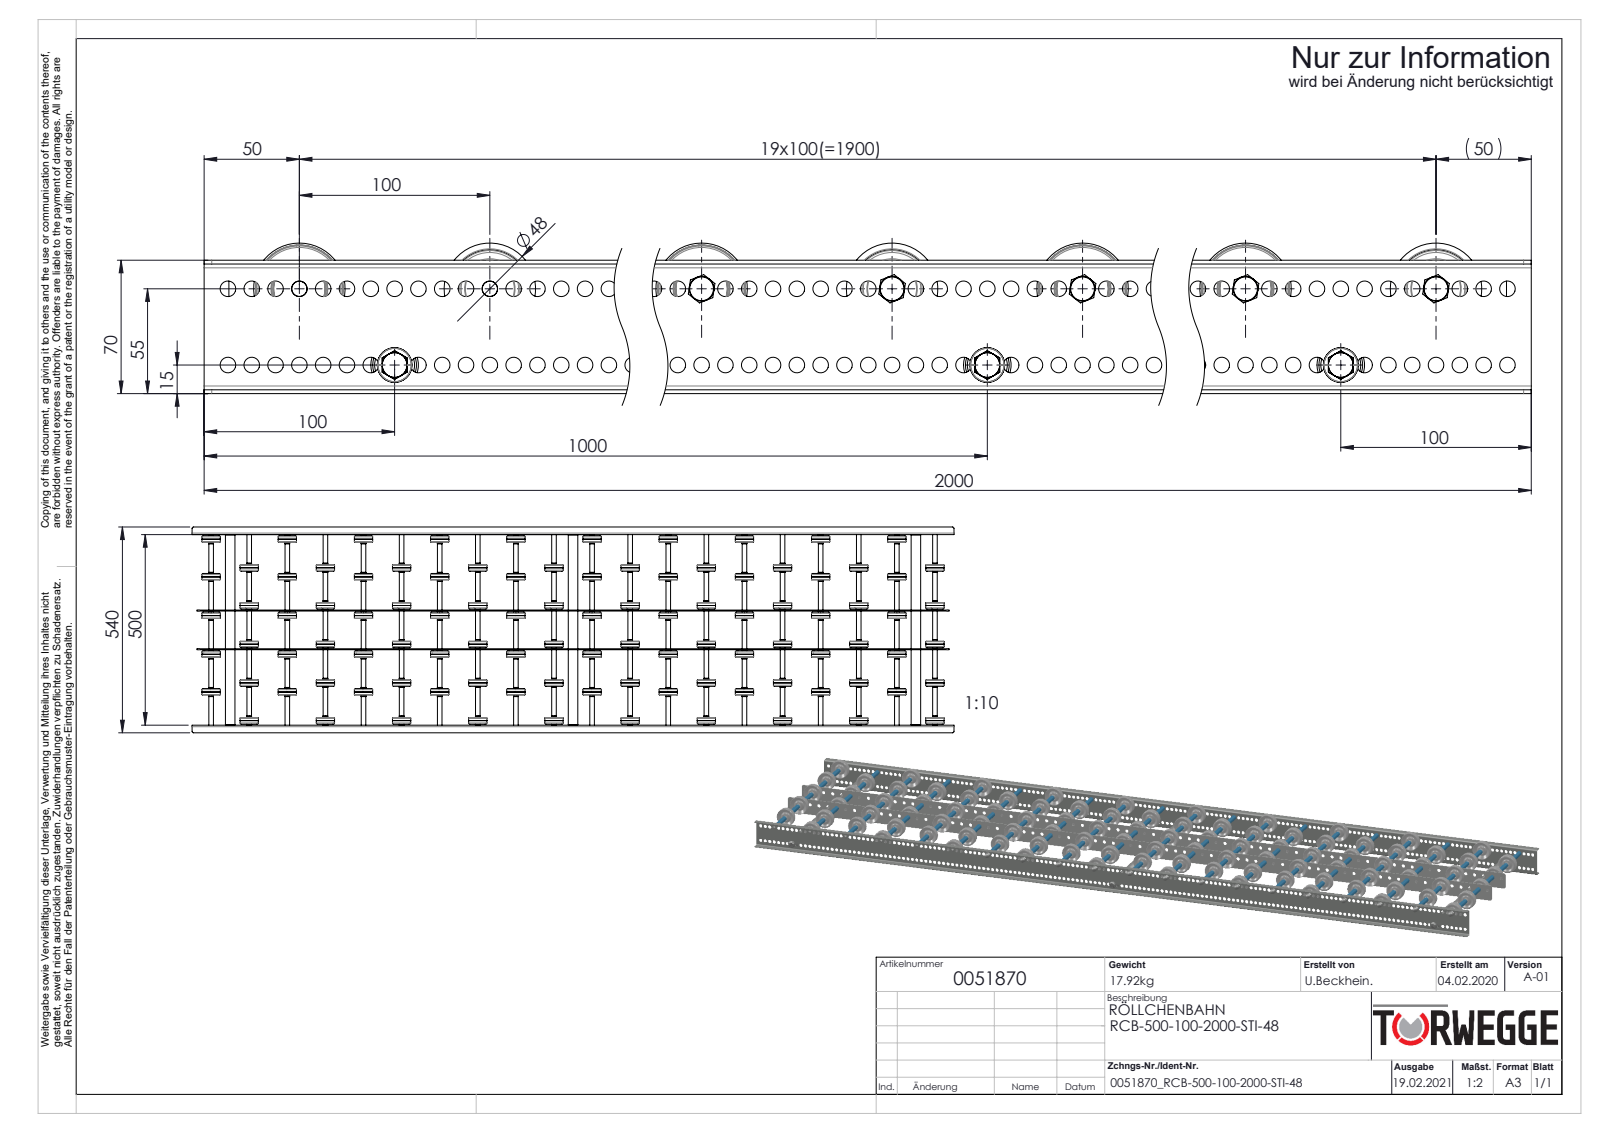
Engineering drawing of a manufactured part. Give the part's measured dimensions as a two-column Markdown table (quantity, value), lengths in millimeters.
| quantity | value |
| --- | --- |
| part name | Profil_LRB-20x70x20x2_KFG_S100202_U-PROFIL-20-70-20-2-LRB-L=2000; Hutmutter_DIN_1587_M8; K0011528_2200-48-8; S100994_Sperrzahnschraube_M08x16-8.8-A2K (+6 more) |
| STEP written by | SolidWorks 2020 (AUTOMOTIVE_DESIGN) |
| units | millimeters |
| bodies | 367 solids, 11522 faces (2238 planar, 4824 cylindrical, 4460 other) |
| overall size | 2000 × 540 × 79 |
| volume | 4 355 000 mm³ |
| surface area | 3 421 000 mm² |
| round holes (diameter × count) | 8.2 × 318, 8.5 × 79, 8 × 20, 9.65 × 20, 15 × 20, 41 × 20, 6.65 × 14, 6.8 × 3, 21 × 3 |
| round bosses / shafts (diameter × count) | 48 × 20, 13 × 20, 12.4 × 20, 12 × 20, 11.5 × 20, 12.5 × 14, 25 × 3, 8 × 3 |
| partial cylindrical surfaces (radius × count) | 4 × 8, 2 × 4, 5 × 4 |
| main face-to-face distances | 2, 101.5, 200.5, 302, 99, 502, 12, 87, 75, 200 |
| hole center spacings | 12.5, 25, 37.5, 50, 62.5, 75, 87.5, 100 |
